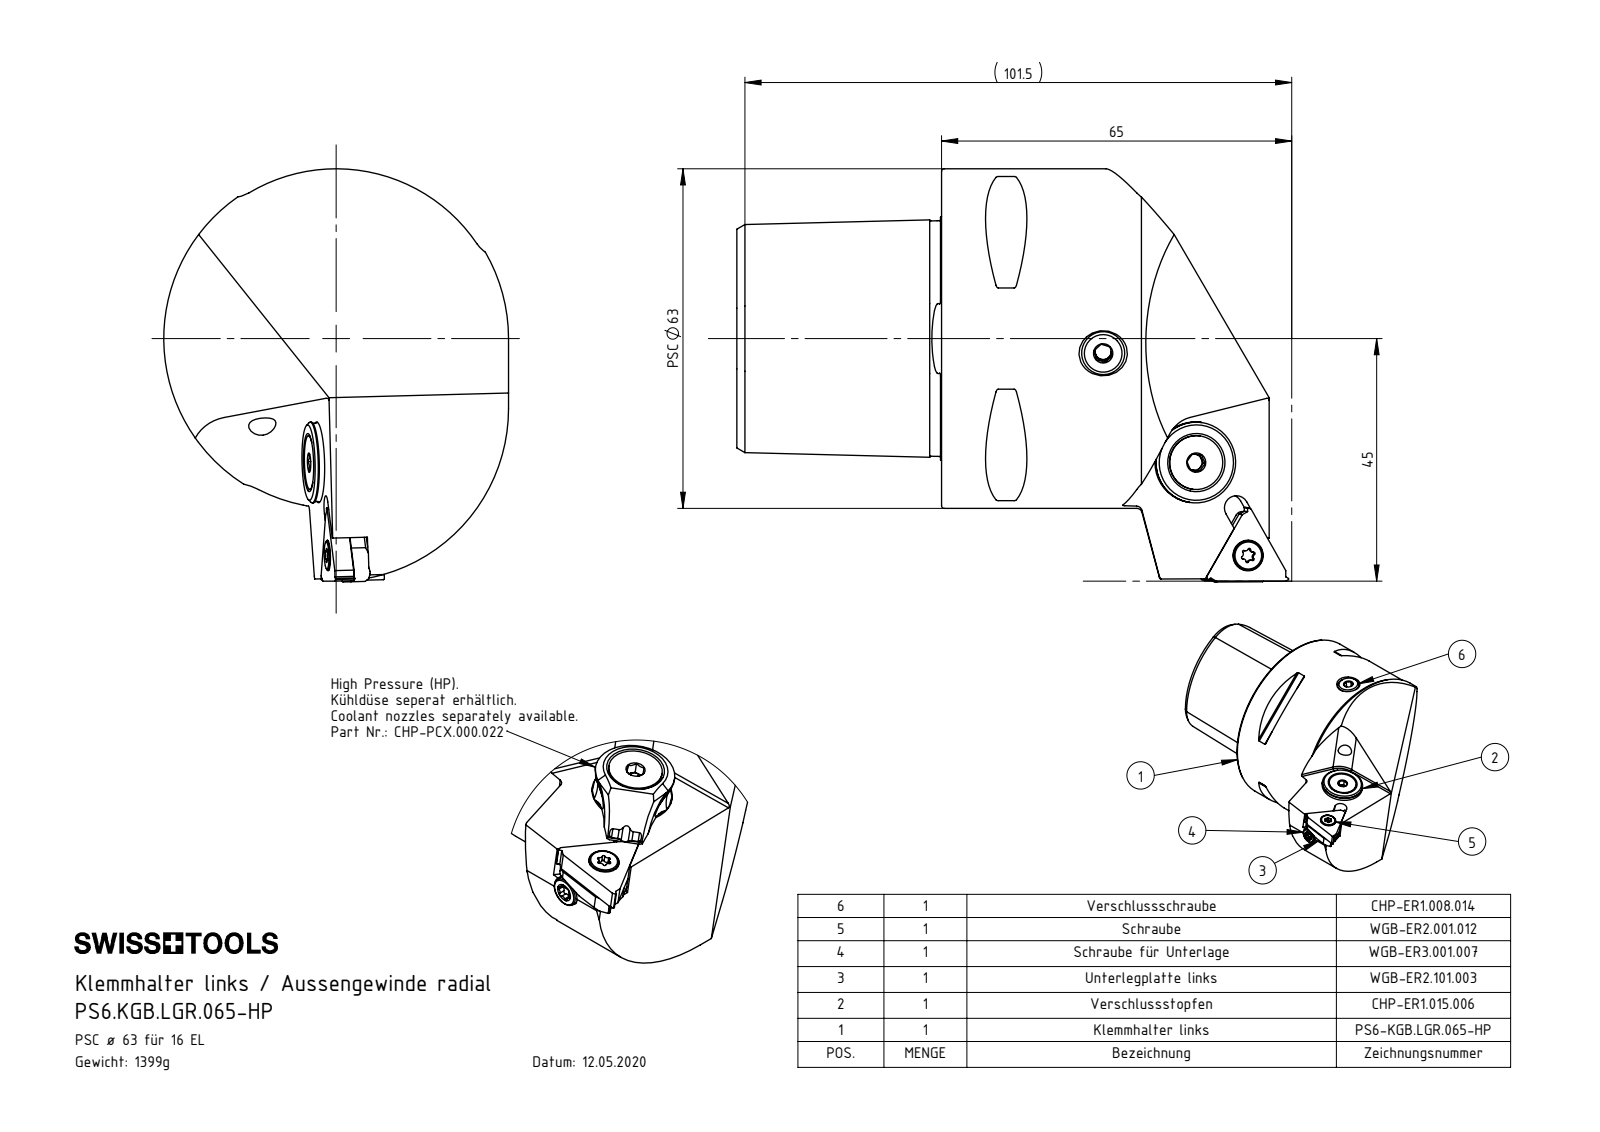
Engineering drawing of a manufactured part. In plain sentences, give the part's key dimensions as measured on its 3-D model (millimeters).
The part is named "LT16EL; PS6-KGB.LGR.065-HP_A_Fertigbearbeitung; WGB-ER2.001.012_A; CHP-ER1.015.006_A (+8 more)". Its 3-D file was written by "SolidWorks 2017 (AUTOMOTIVE_DESIGN)". It is 10 solids with 311 faces: 127 planar, 84 cylindrical and 100 other. Overall it measures 102.41 by 76.66 by 64 millimeters. Its volume is 178 236 cubic millimeters and its surface area 32 084 square millimeters. Round holes: 2 of diameter 2.58, 2 of diameter 4, 2 of diameter 4.2, 2 of diameter 5, 1 of diameter 1.2, 1 of diameter 2, 1 of diameter 2.5, 1 of diameter 3, 1 of diameter 4.02, 1 of diameter 5.2, 1 of diameter 7, 1 of diameter 8.1. Round bosses or shafts: 3 of diameter 5.5, 1 of diameter 63, 1 of diameter 15, 1 of diameter 13.4, 1 of diameter 10, 1 of diameter 8, 1 of diameter 5, 1 of diameter 3.18. Partial cylindrical surfaces (rounded edges, fillets, slot ends): 10 of radius 0.5, 6 of radius 0.23, 6 of radius 0.34, 6 of radius 0.57, 6 of radius 0.57, 2 of radius 0.1, 2 of radius 0.25, 2 of radius 32. The main face-to-face distances are 38, 24.88, 4.79, 27, 11, 1.45, 3.34, 55.8, 6.53, 1.74. The hole center spacings are 17.3, 17.32, 20, 4.5, 4.52, 4.54, 4.56, 17.11.
